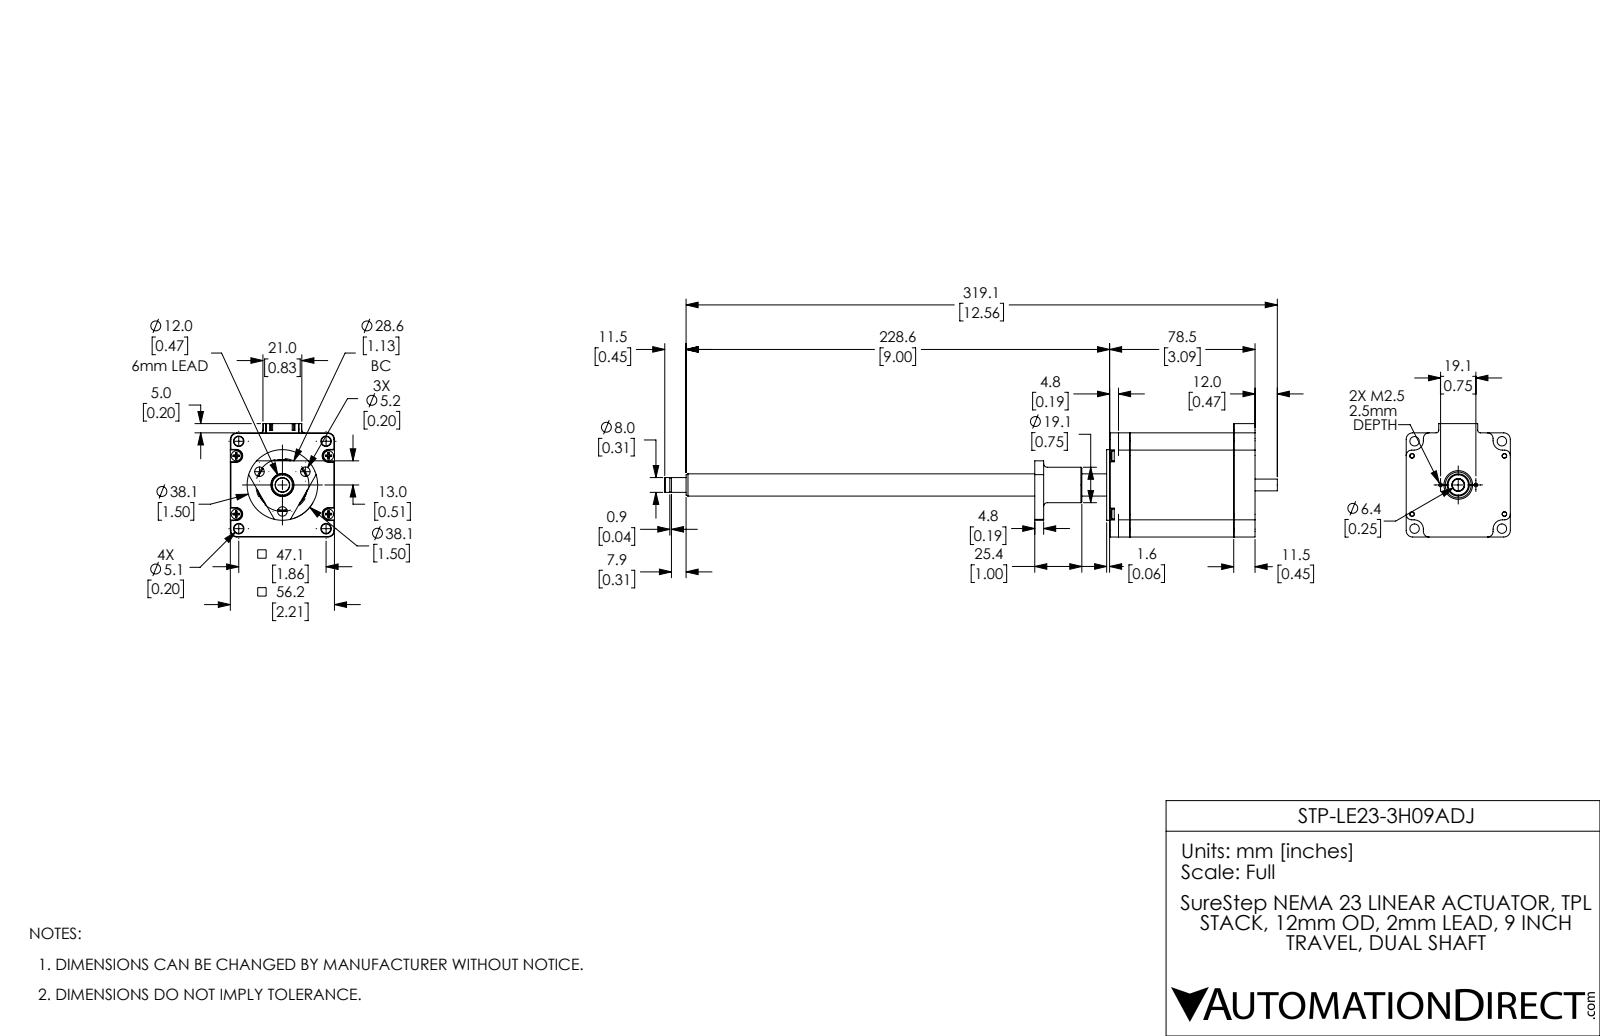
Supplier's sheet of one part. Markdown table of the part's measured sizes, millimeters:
| quantity | value |
| --- | --- |
| part name | STP-LE23-3H09ADJ_2; STP-LE23-3H09ADJ_1; STP-LE23-3H09ADJ |
| STEP written by | SolidWorks 2017 (AUTOMOTIVE_DESIGN) |
| units | millimeters |
| bodies | 7 solids, 1001 faces (380 planar, 460 cylindrical, 161 other) |
| overall size | 330.6 × 61.2 × 56.2 |
| volume | 234 479 mm³ |
| surface area | 65 956 mm² |
| round holes (diameter × count) | 4.5 × 8, 2.5 × 4, 3.3 × 4, 5.1 × 4, 5.16 × 3, 2 × 2, 2.05 × 2, 6.9 × 1, 10.5 × 1, 14.8 × 1, 15.5 × 1, 16 × 1 |
| round bosses / shafts (diameter × count) | 5.4 × 4, 2.91 × 4, 38.1 × 1, 36 × 1, 35.6 × 1, 34.85 × 1, 28 × 1, 19.1 × 1 |
| partial cylindrical surfaces (radius × count) | 1.5 × 10, 0.2 × 8, 3 × 8, 1.8 × 4, 3.2 × 4, 3.5 × 4, 5 × 4, 0.6 × 1 |
| main face-to-face distances | 56.2, 56, 11.5, 67.5, 78.5, 11, 51.4, 67, 1.6, 1.1 |
| hole center spacings | 24.75, 14.12, 33.05, 35.01, 45.74, 48.53, 56.99, 6.55 |
